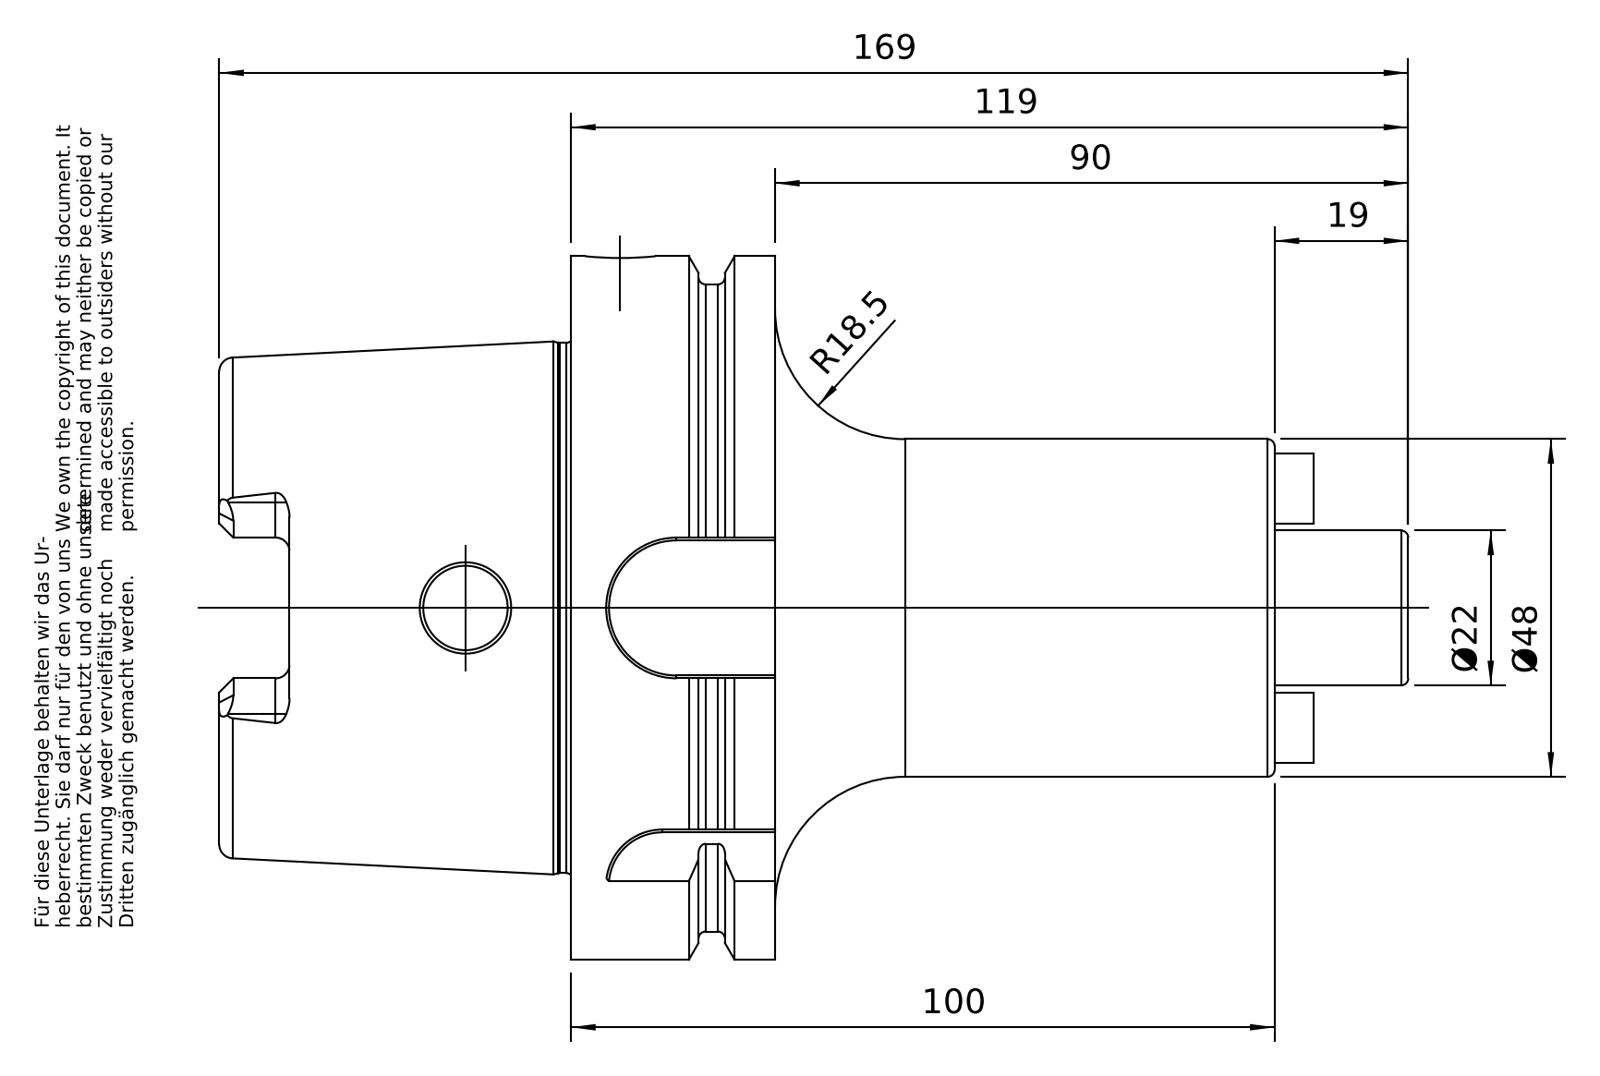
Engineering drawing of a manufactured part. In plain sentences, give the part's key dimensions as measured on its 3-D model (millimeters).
The part is named "A100-051-22". Its 3-D file was written by "PRO/ENGINEER BY PARAMETRIC TECHNOLOGY CORPORATION, 2010430 (CONFIG_CONTROL_DESIGN)". It is 1 solid with 191 faces: 61 planar, 55 cylindrical and 75 other. Overall it measures 169 by 100 by 100 millimeters. Its volume is 402 220 cubic millimeters and its surface area 63 086 square millimeters. Round holes: 2 of diameter 10, 1 of diameter 8.5, 1 of diameter 12, 1 of diameter 22.5, 1 of diameter 24, 1 of diameter 24.32, 1 of diameter 24.5, 1 of diameter 53, 1 of diameter 63. Round bosses or shafts: 1 of diameter 100, 1 of diameter 92, 1 of diameter 75.36, 1 of diameter 48, 1 of diameter 22. Partial cylindrical surfaces (rounded edges, fillets, slot ends): 6 of radius 2, 4 of radius 5, 1 of radius 8, 1 of radius 10, 1 of radius 11. The main face-to-face distances are 29, 12.5, 16.5, 100, 87.5, 71, 50, 62.5, 79, 150.
